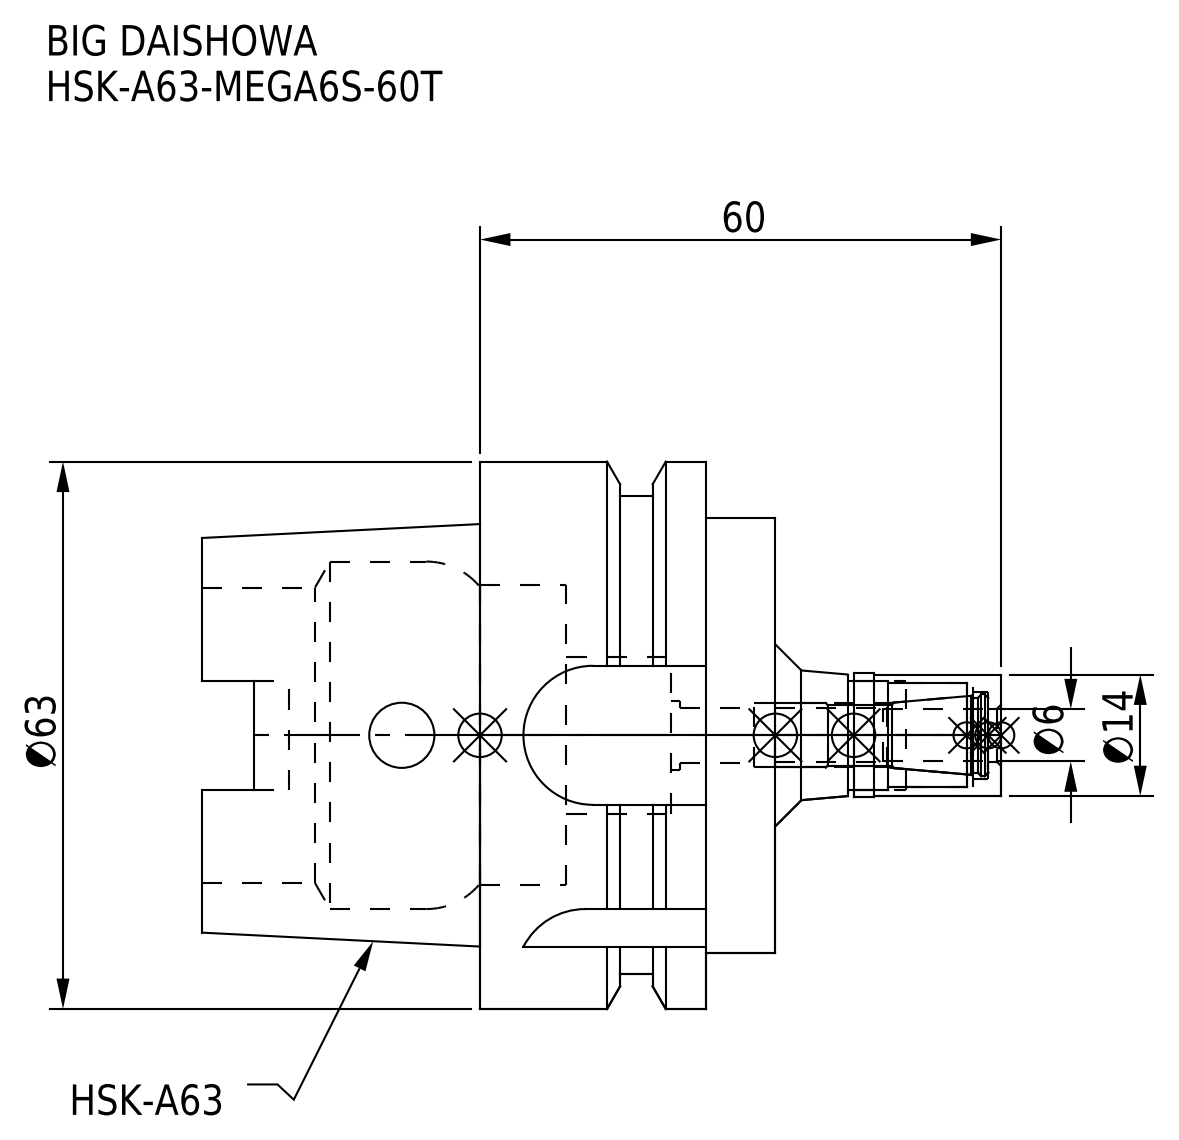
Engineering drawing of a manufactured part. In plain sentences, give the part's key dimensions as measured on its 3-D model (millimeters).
The part is named "HSK-A63-MEGA6S-60T-060.stp; MGN6S_1.stp; DXF_TEMP_ASSY_ASM_4_ASM.stp; HA63MS06060T-060_ASM.stp (+3 more)". Its 3-D file was written by "SolidWorks 2019 (CONFIG_CONTROL_DESIGN)". It is 2 solids with 122 faces: 47 planar, 53 cylindrical and 22 other. Overall it measures 92 by 63 by 63 millimeters. Its volume is 100 091 cubic millimeters and its surface area 26 709 square millimeters. Round holes: 1 of diameter 6.1, 1 of diameter 6.4, 1 of diameter 7.4, 1 of diameter 7.5, 1 of diameter 8, 1 of diameter 10, 1 of diameter 12, 1 of diameter 12.5, 1 of diameter 18, 1 of diameter 34, 1 of diameter 34.5, 1 of diameter 40. Round bosses or shafts: 1 of diameter 63, 1 of diameter 55, 1 of diameter 50, 1 of diameter 14.3, 1 of diameter 14. Partial cylindrical surfaces (rounded edges, fillets, slot ends): 4 of radius 2.88, 4 of radius 8. The main face-to-face distances are 34, 26, 8, 24.05, 16.05, 9.95, 66, 58, 41.95, 32.
